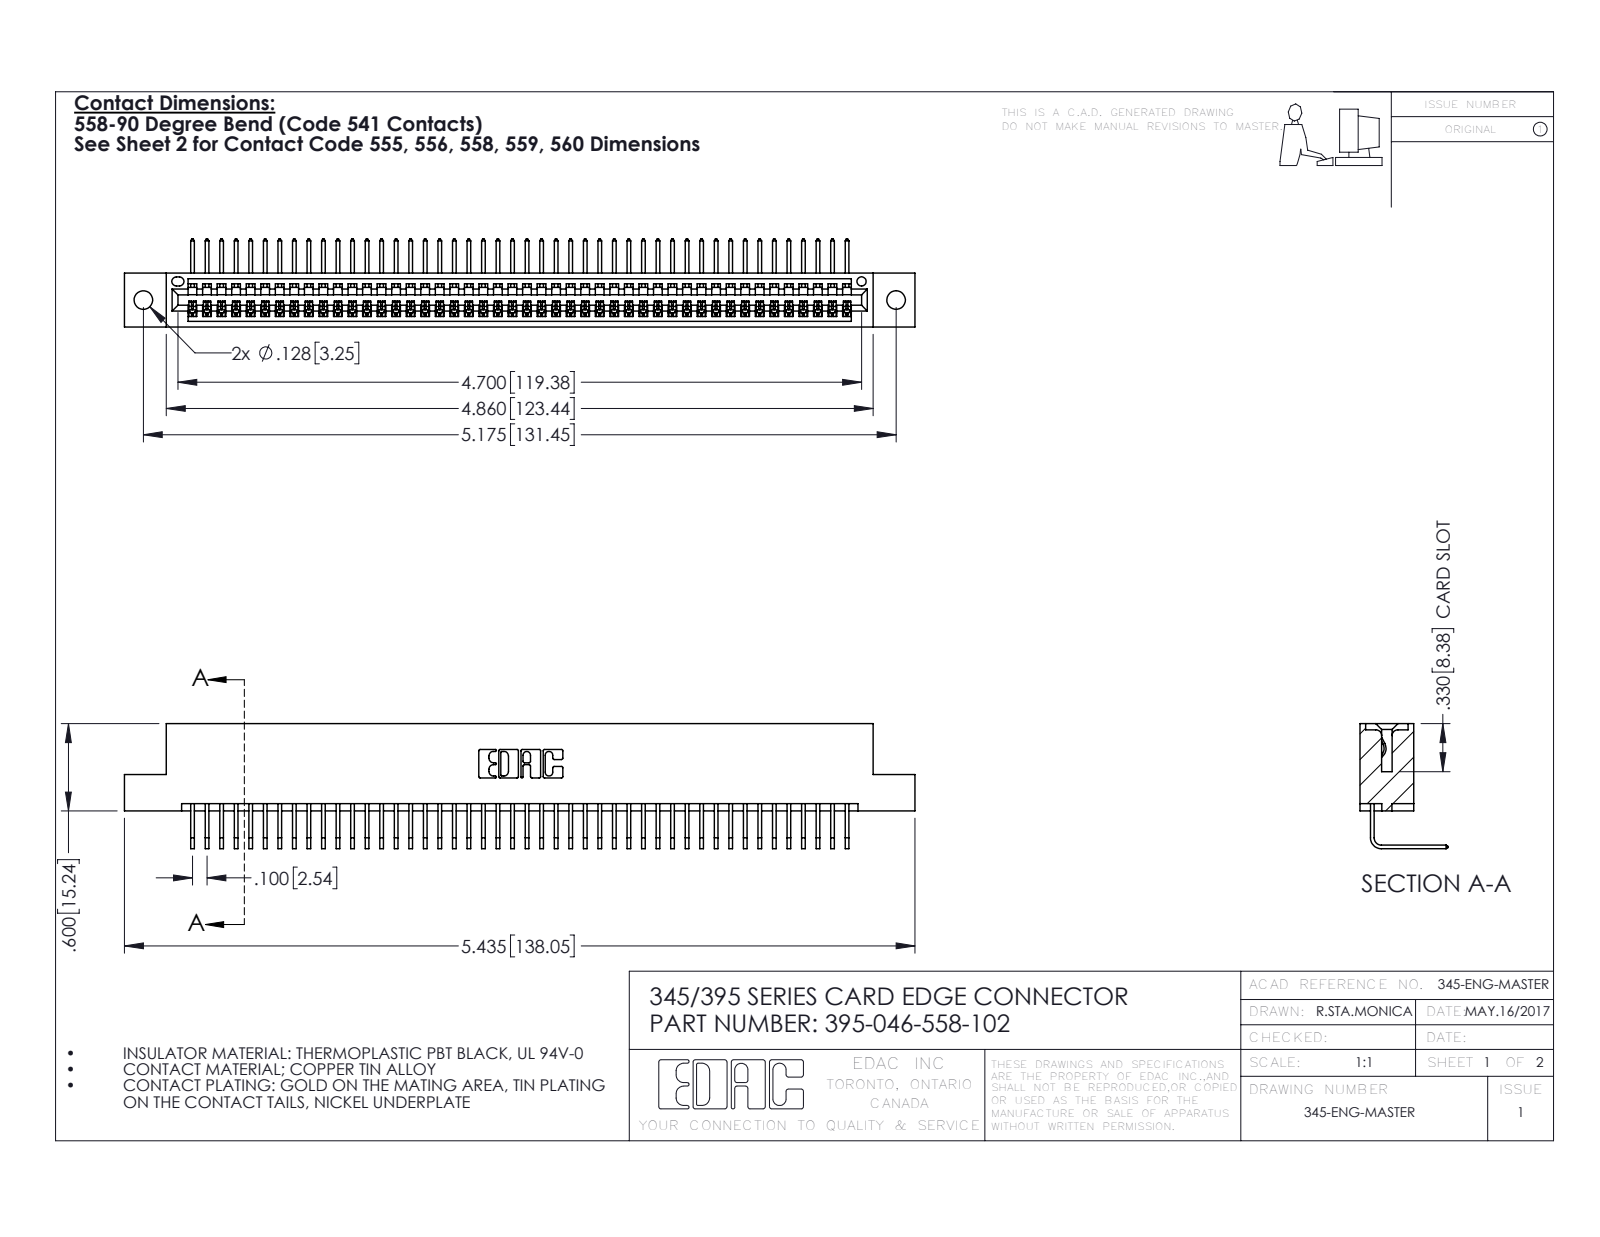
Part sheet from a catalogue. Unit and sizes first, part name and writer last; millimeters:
Units: millimetres
Overall size (bounding box): 138 × 21.8 × 15.4
Round holes (diameter × count): ⌀3.3 ×2, ⌀1.6 ×1
Partial cylindrical surfaces — rounded edges, fillets, slot ends (radius × count): R0.2 ×92, R0.3 ×22, R0.2 ×6, R0.8 ×6, R0.7 ×3, R0.8 ×2, R1 ×2, R0.4 ×1
Main face-to-face distances: 7.6, 1.8, 9.4, 5.1, 2.5, 6.9, 0.6, 5.7, 3.8, 1.8
Hole centre spacings: 6.9, 125.5, 131.4
Volume: 13 300 mm³ · Surface area: 18 310 mm²
Bodies: 47 solids, 2886 faces (2012 planar, 874 cylindrical, 0 other)
Part name (STEP PRODUCT): 395-046-558-102; 345-292-001_558 Tail - 2; 345 Part_Flush Mounting Lugs - 0.128 Dia
STEP written by: SolidWorks 2016 (CONFIG_CONTROL_DESIGN)
